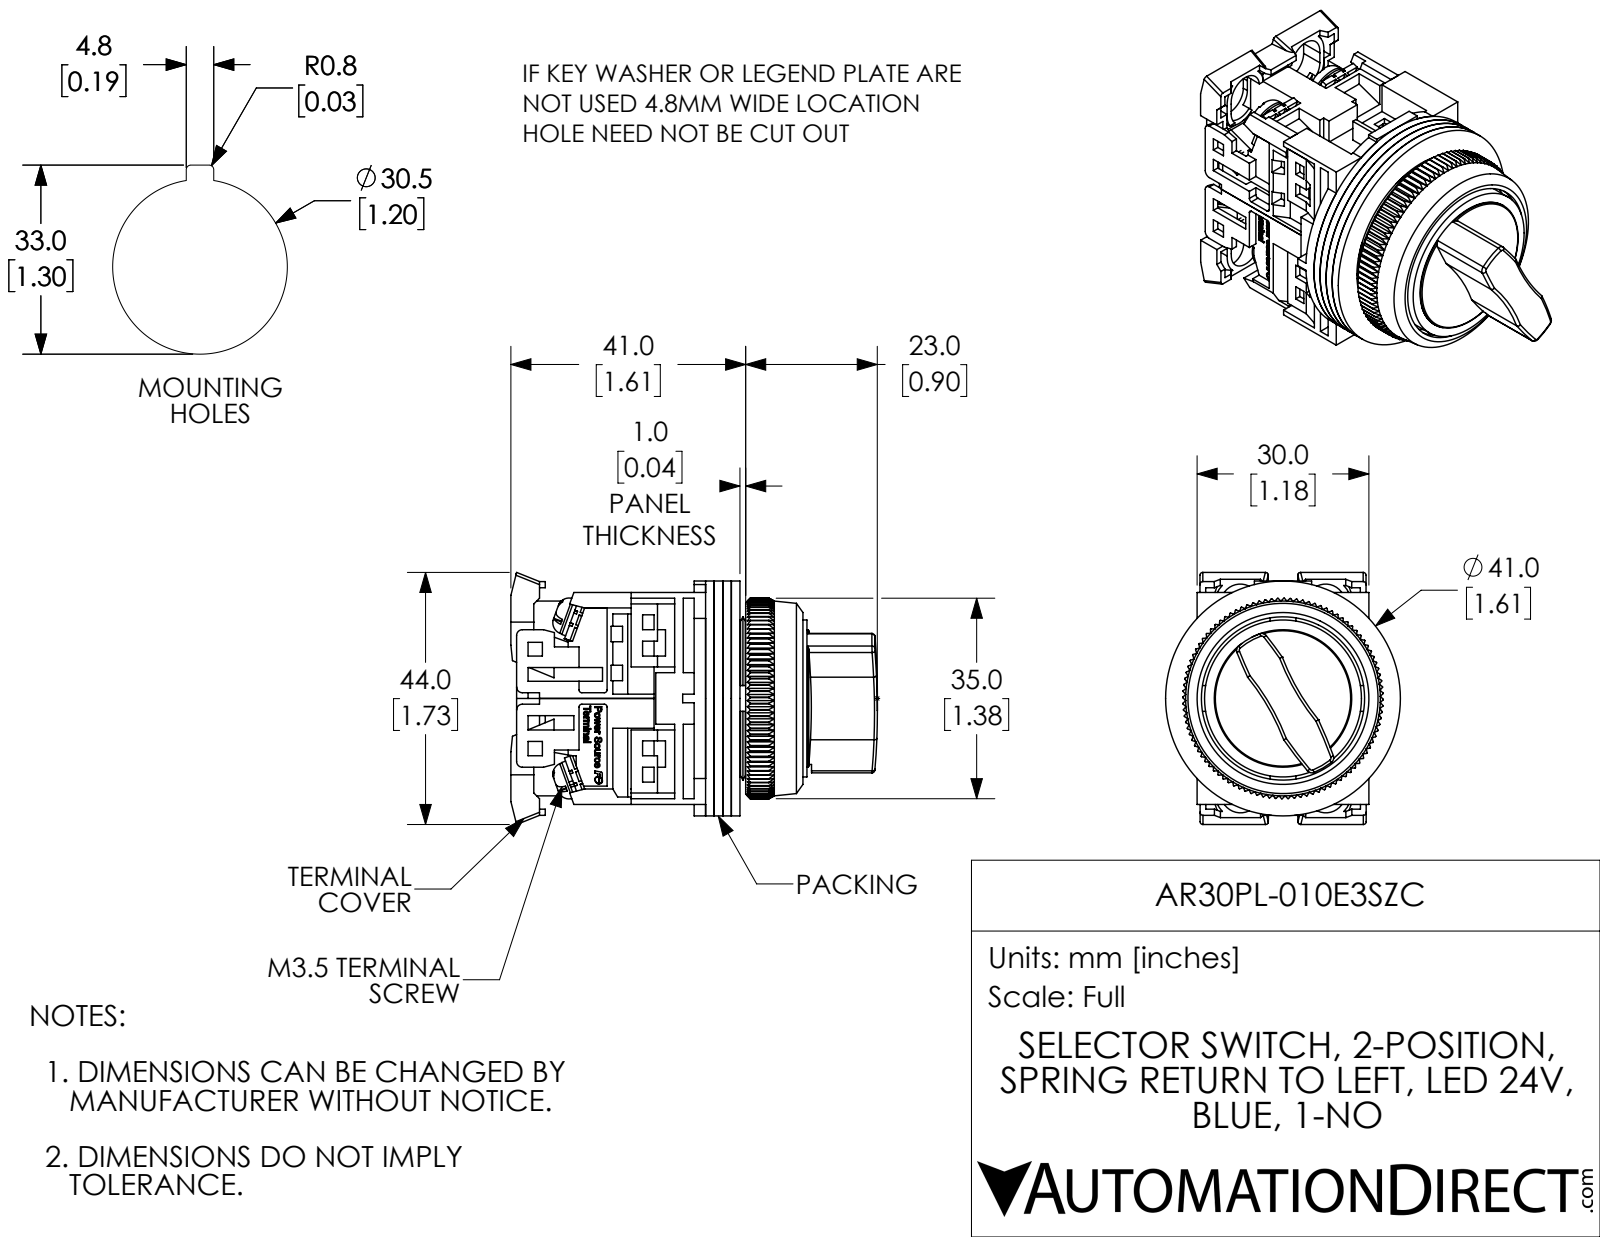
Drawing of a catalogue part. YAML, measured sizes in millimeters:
part_name: "AR30PL-010E3SZC"
step_written_by: "SolidWorks 2017 (AUTOMOTIVE_DESIGN)"
units: millimeters
bodies: {solids: 25, faces: 2434, planar: 1731, cylindrical: 305, other: 398}
overall_size: [64, 44, 41]
volume: 36670
surface_area: 38260
round_holes:
  - {diameter: 3.5, count: 8}
  - {diameter: 3.6, count: 4}
  - {diameter: 3, count: 1}
  - {diameter: 12, count: 1}
  - {diameter: 18, count: 1}
  - {diameter: 19.5, count: 1}
  - {diameter: 21, count: 1}
  - {diameter: 28.5, count: 1}
  - {diameter: 30, count: 1}
  - {diameter: 31.8, count: 1}
round_bosses_or_shafts:
  - {diameter: 6.6, count: 4}
  - {diameter: 3.5, count: 4}
  - {diameter: 1.6, count: 2}
  - {diameter: 41, count: 1}
  - {diameter: 29.2, count: 1}
  - {diameter: 27.4, count: 1}
  - {diameter: 24, count: 1}
  - {diameter: 22.5, count: 1}
partial_cylinders:
  - {radius: 1.5, count: 16}
  - {radius: 0.5, count: 12}
  - {radius: 1, count: 8}
  - {radius: 3.5, count: 4}
  - {radius: 4.5, count: 4}
  - {radius: 3, count: 2}
  - {radius: 40, count: 2}
  - {radius: 75, count: 2}
face_to_face_distances: [1.5, 3, 4.5, 1, 2, 36, 34.5, 20.6, 5, 0.5]
hole_center_spacings: [14.7, 15.5]
